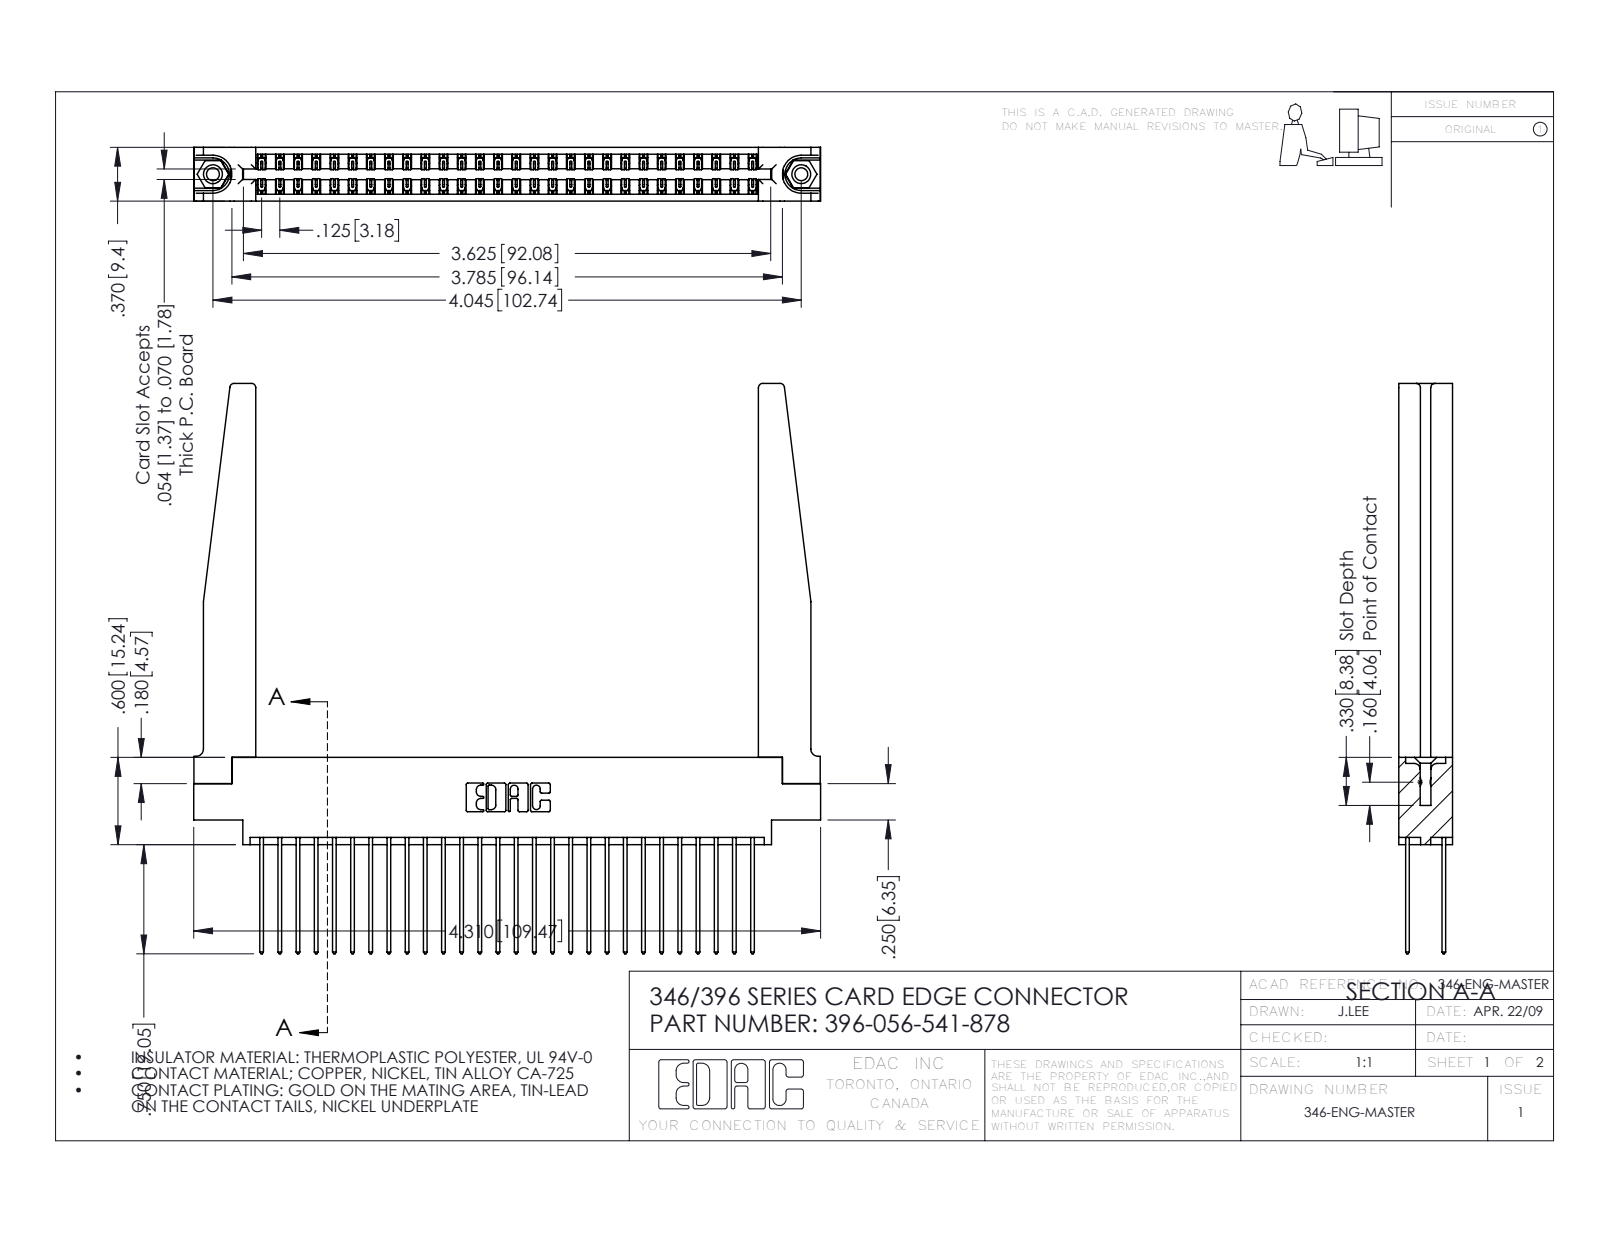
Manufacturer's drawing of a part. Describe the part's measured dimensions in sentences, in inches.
The part is named "396-056-541-878; 345-292-001_345-293-141; 346-220-078_345-220-078; 346 Part_0.170 Offset - 0.156 Dia-TH (+1 more)". Its 3-D file was written by "SolidWorks 2016 (CONFIG_CONTROL_DESIGN)". It is 61 solids with 3272 faces: 2182 planar, 1038 cylindrical and 52 other. Overall it measures 4.31 by 3.92 by 0.37 inches. Its volume is 1.077 cubic inches and its surface area 35.33 square inches. Round holes: 2 of diameter 0.089, 2 of diameter 0.125, 2 of diameter 0.156, 1 of diameter 0.064. Round bosses or shafts: 2 of diameter 0.155. Partial cylindrical surfaces (rounded edges, fillets, slot ends): 84 of radius 0.006, 56 of radius 0.01, 22 of radius 0.01, 8 of radius 0.03, 6 of radius 0.007, 6 of radius 0.031, 3 of radius 0.026, 2 of radius 0.014. The main face-to-face distances are 0.37, 0.048, 0.322, 0.072, 0.25, 0.298, 0.025, 0.15, 0.148, 0.275. The hole center spacings are 0.246, 3.837, 4.045.
